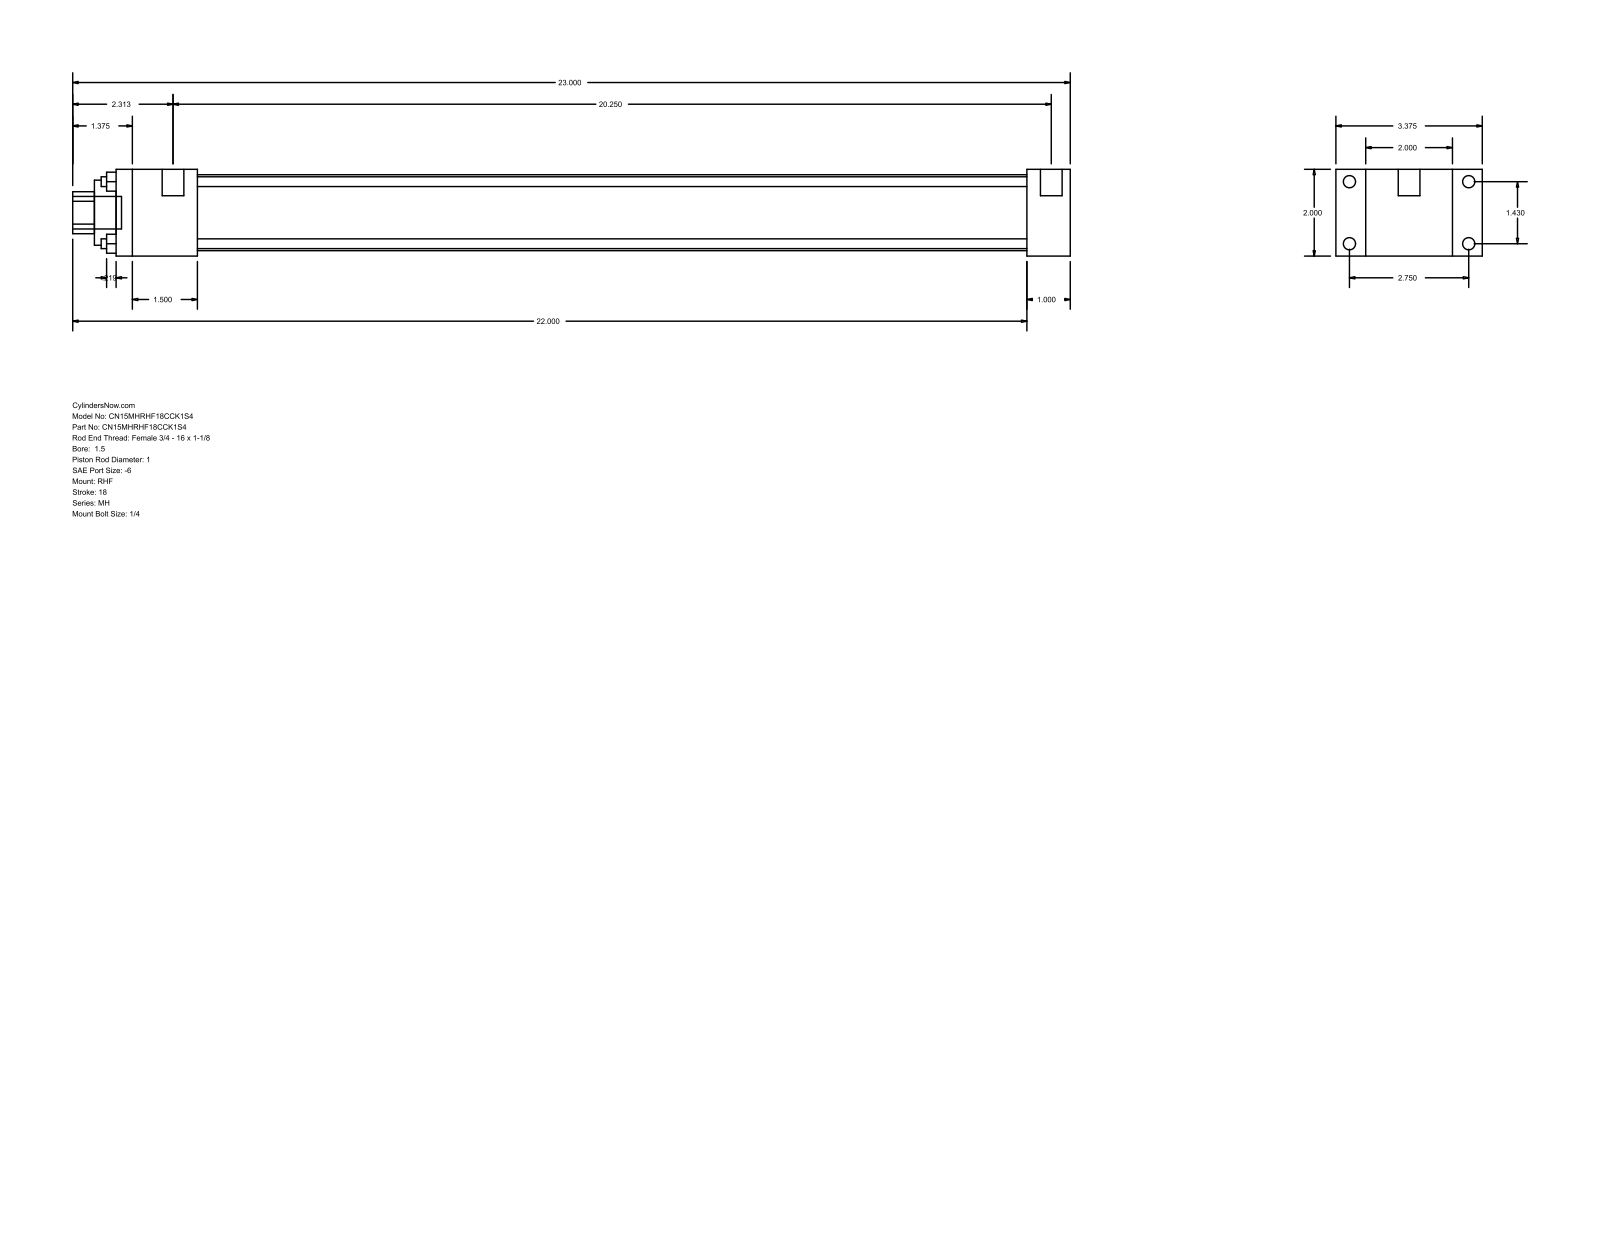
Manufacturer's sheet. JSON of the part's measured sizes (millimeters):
{"part_name": "MH_RHF__0150_1", "step_written_by": "GSSL Pune (CONFIG_CONTROL_DESIGN)", "units": "millimeters", "bodies": {"solids": 0, "faces": 88, "planar": 60, "cylindrical": 28, "other": 0}, "overall_size": [584.2, 85.72, 50.8], "round_holes": [[5.71, 4], [25.4, 1], [38.1, 1], [44.45, 1]], "round_bosses_or_shafts": [[7.14, 4], [5.56, 4], [12.7, 2], [19.05, 1]], "partial_cylinders_radius": [[12.29, 1]], "face_to_face_distances": [50.8, 25.4, 17.46, 68.26, 85.72, 558.8, 533.4, 47.63, 485.77, 511.17], "hole_center_spacings": [25.68, 36.32, 51.36]}
